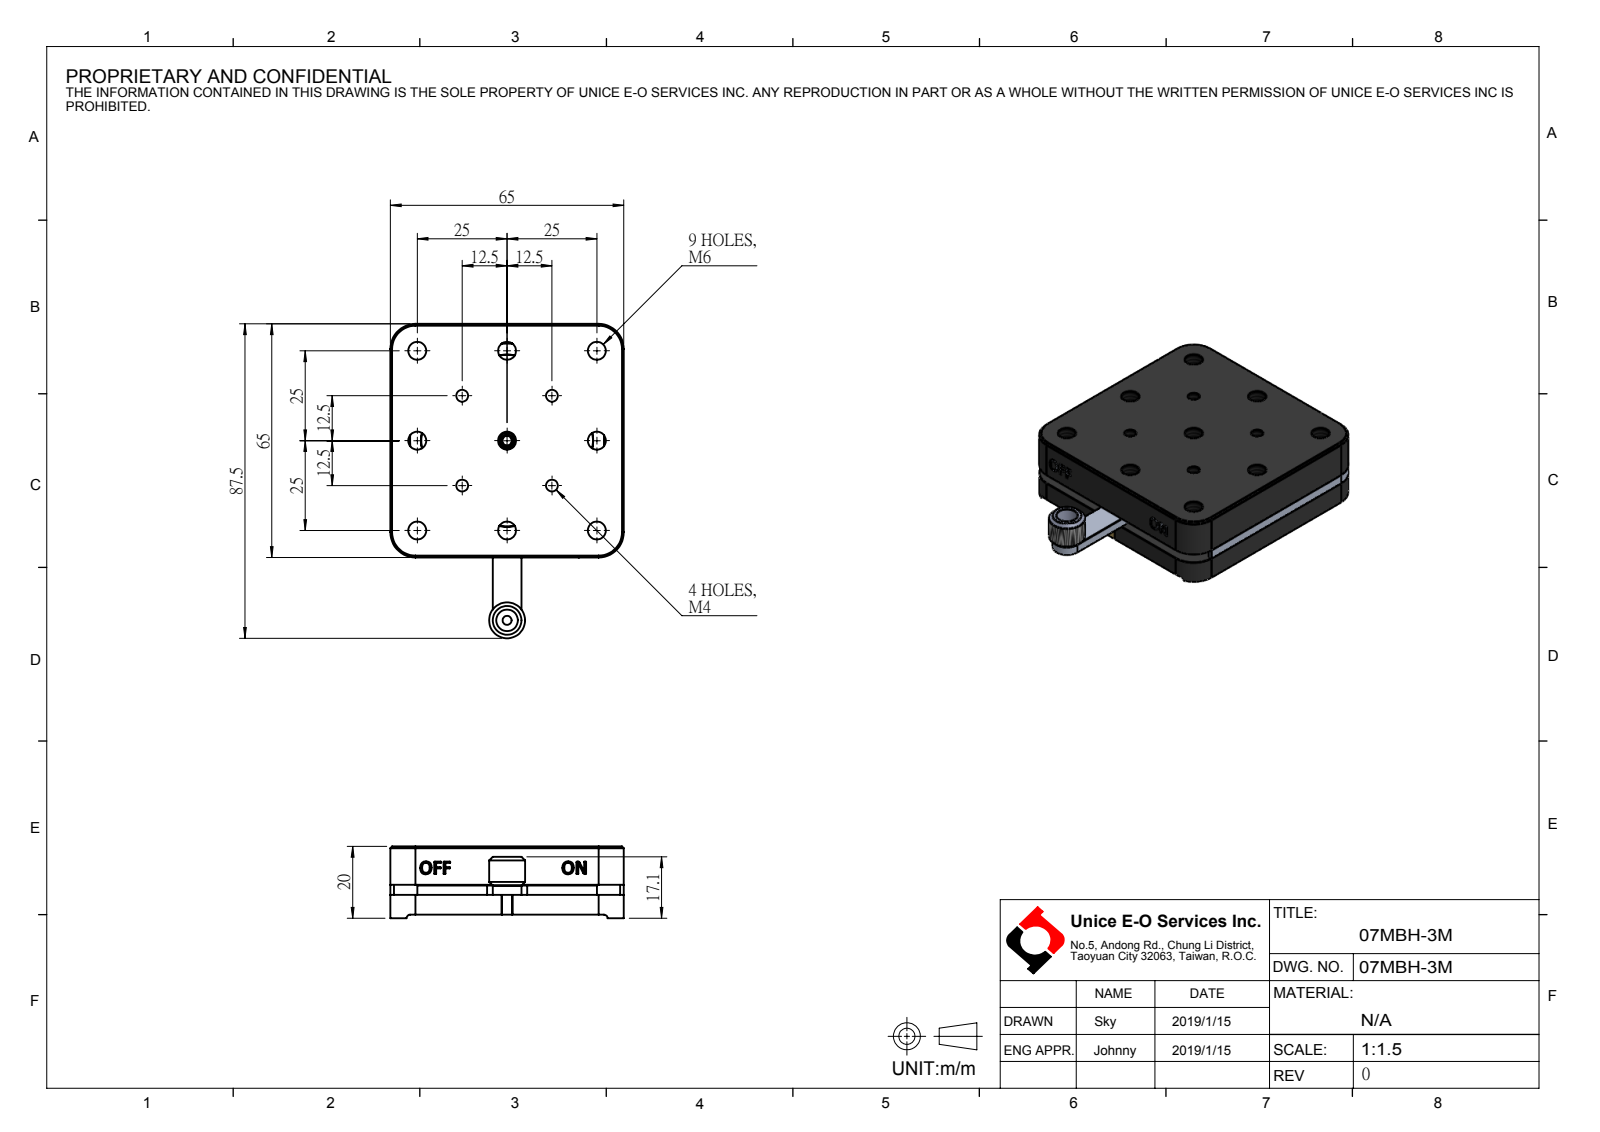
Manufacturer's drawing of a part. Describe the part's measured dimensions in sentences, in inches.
The part is named "07MBH-3M". Its 3-D file was written by "SolidWorks 2016 (AUTOMOTIVE_DESIGN)". It is 0 solids with 177 faces: 95 planar, 61 cylindrical and 21 other. Overall it measures 3.445 by 2.559 by 0.787 inches. Round holes: 9 of diameter 0.197, 7 of diameter 0.236, 4 of diameter 0.13, 1 of diameter 0.098. Round bosses or shafts: 1 of diameter 0.394. Partial cylindrical surfaces (rounded edges, fillets, slot ends): 4 of radius 0.276, 2 of radius 0.039, 1 of radius 0.157. The main face-to-face distances are 0.11, 0.531, 0.421, 0.217, 0.327, 0.748, 2.559, 0.319, 0.102, 0.429. The hole center spacings are 0.696, 1.556, 0.984, 1.392, 2.201, 1.969, 2.088, 0.355.
